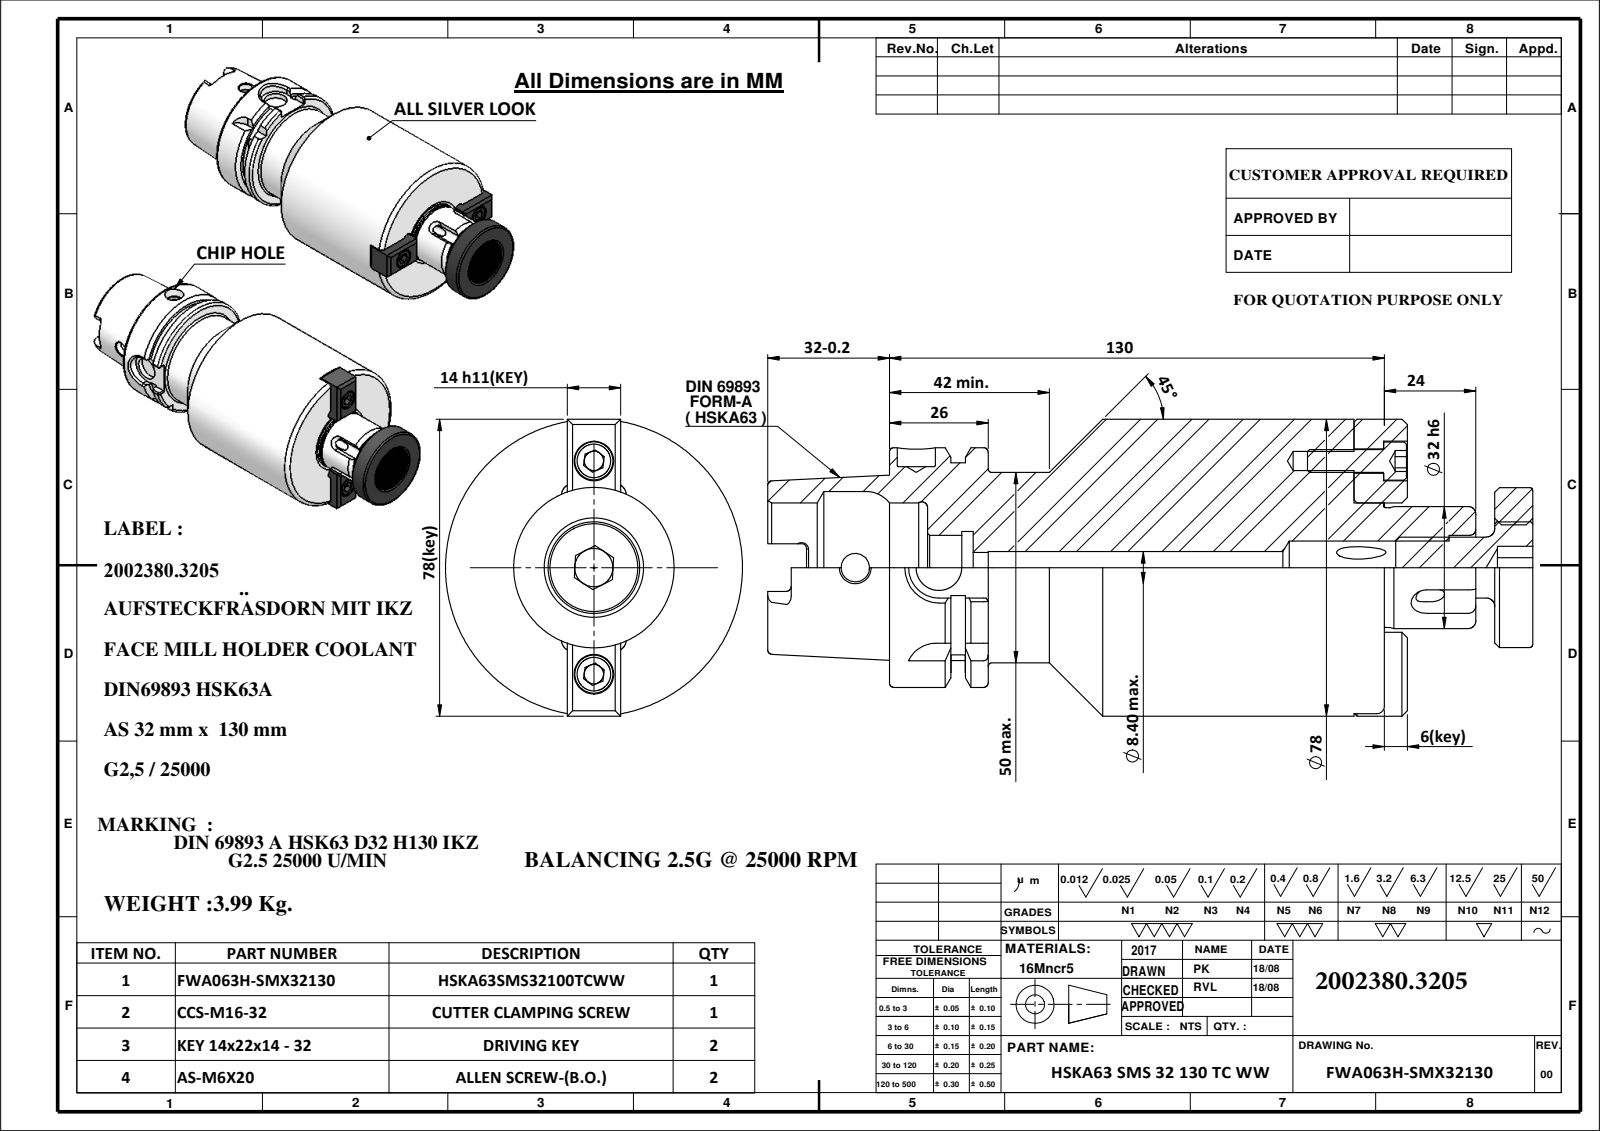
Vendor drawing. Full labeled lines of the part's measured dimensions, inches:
Part name (STEP PRODUCT): CCS-M16-32; 9163A-AS532130; HSKA63SMS32130TCWW; CCS-M16-32-2 (+2 more)
STEP written by: SolidWorks 2009 (CONFIG_CONTROL_DESIGN)
Units: inches
Bodies: 7 solids, 383 faces (148 planar, 105 cylindrical, 130 other)
Overall size (bounding box): 7.913 × 3.071 × 3.071
Volume: 32.78 in³ · Surface area: 109.1 in²
Round holes (diameter × count): ⌀0.157 ×4, ⌀0.197 ×2, ⌀0.252 ×2, ⌀0.409 ×2, ⌀0.295 ×1, ⌀0.315 ×1, ⌀0.331 ×1, ⌀0.394 ×1, ⌀0.472 ×1, ⌀0.551 ×1, ⌀0.669 ×1, ⌀0.748 ×1
Round bosses / shafts (diameter × count): ⌀0.394 ×2, ⌀0.236 ×2, ⌀3.071 ×1, ⌀2.48 ×1, ⌀2.165 ×1, ⌀1.969 ×1, ⌀1.654 ×1, ⌀1.26 ×1
Partial cylindrical surfaces — rounded edges, fillets, slot ends (radius × count): R0.118 ×8, R0.051 ×6, R0.113 ×4, R0.315 ×2, R0.354 ×1
Main face-to-face distances: 0.394, 6.26, 0.551, 1.85, 0.315, 1.535, 4.803, 5.118, 6.654, 1.457
Hole centre spacings: 1.102, 0.866, 2.205
